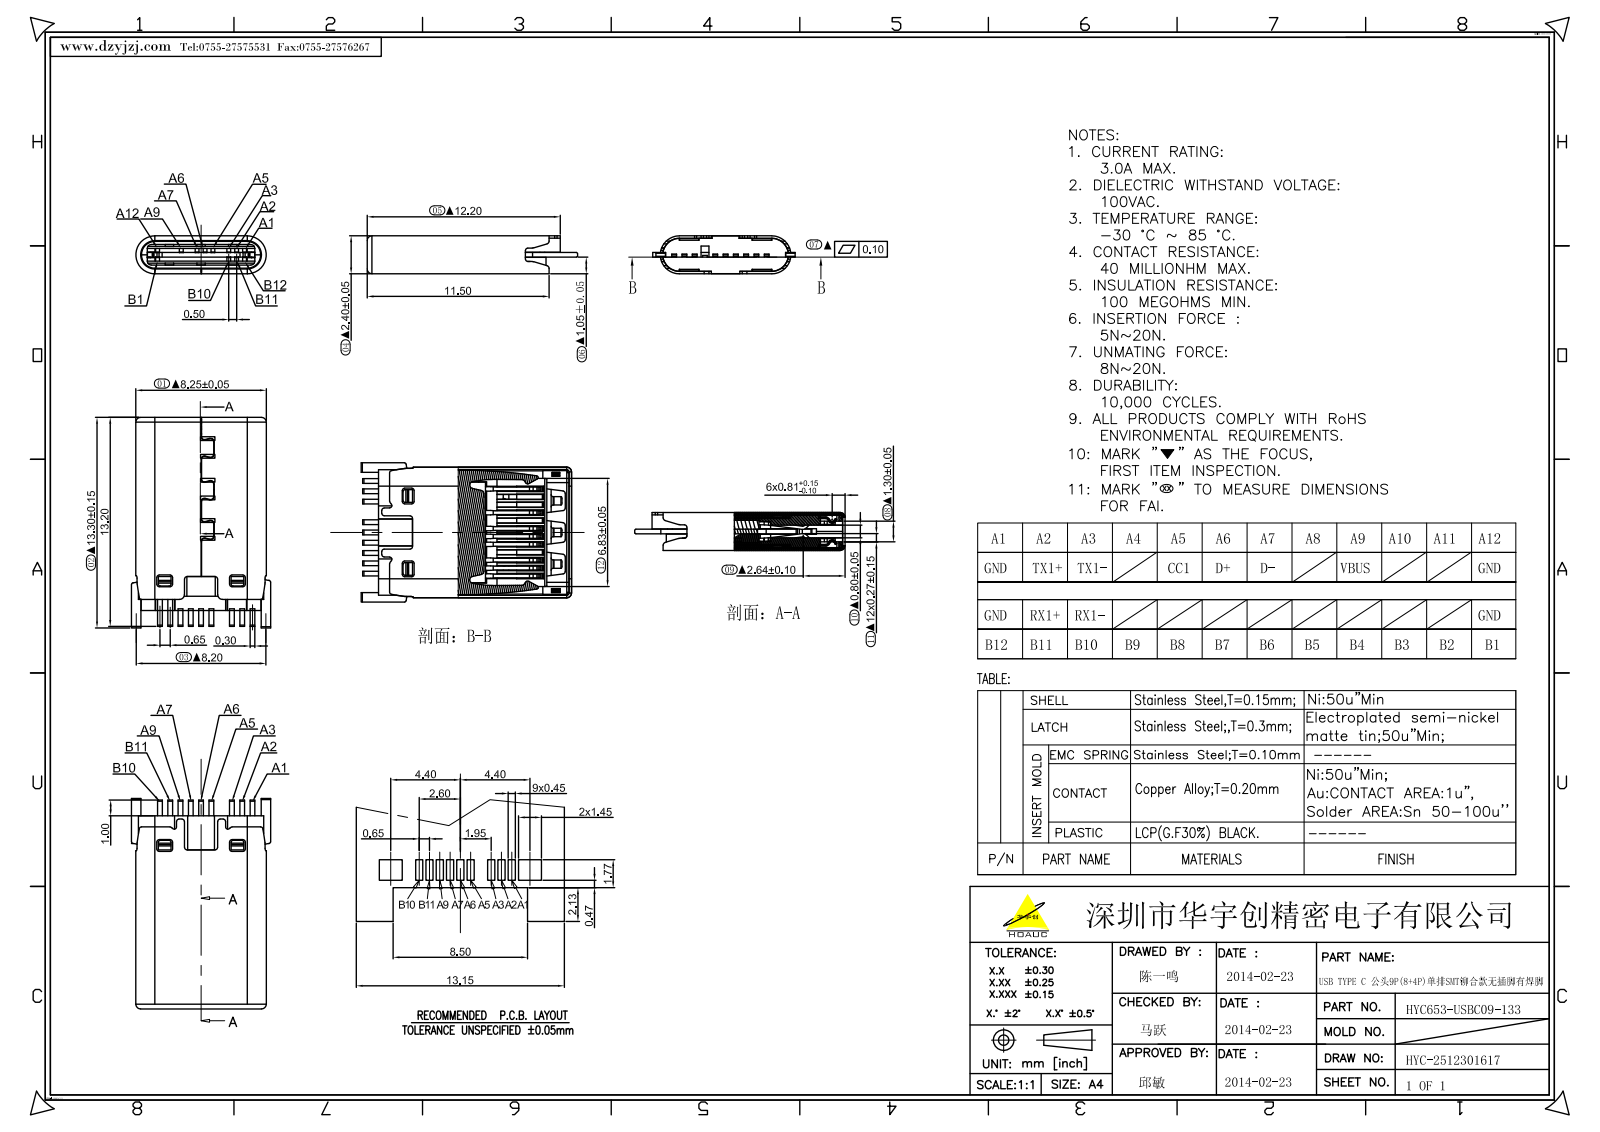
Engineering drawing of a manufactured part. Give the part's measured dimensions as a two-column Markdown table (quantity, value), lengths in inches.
| quantity | value |
| --- | --- |
| part name | XDS-A_TC_2_M_215E-ASM |
| STEP written by | CREO PARAMETRIC BY PTC INC, 2022073 (CONFIG_CONTROL_DESIGN) |
| units | inches |
| bodies | 1 solid, 484 faces (332 planar, 148 cylindrical, 4 other) |
| overall size | 0.524 × 0.346 × 0.094 |
| volume | 0.011 in³ |
| surface area | 0.629 in² |
| partial cylindrical surfaces (radius × count) | 0.006 × 32, 0.008 × 12, 0.004 × 8, 0.012 × 8, 0.007 × 6, 0.009 × 6, 0.01 × 6, 0.041 × 4 |
| main face-to-face distances | 0.031, 0.094, 0.063, 0.041, 0.022, 0.02, 0.073, 0.053, 0.035, 0.051 |
